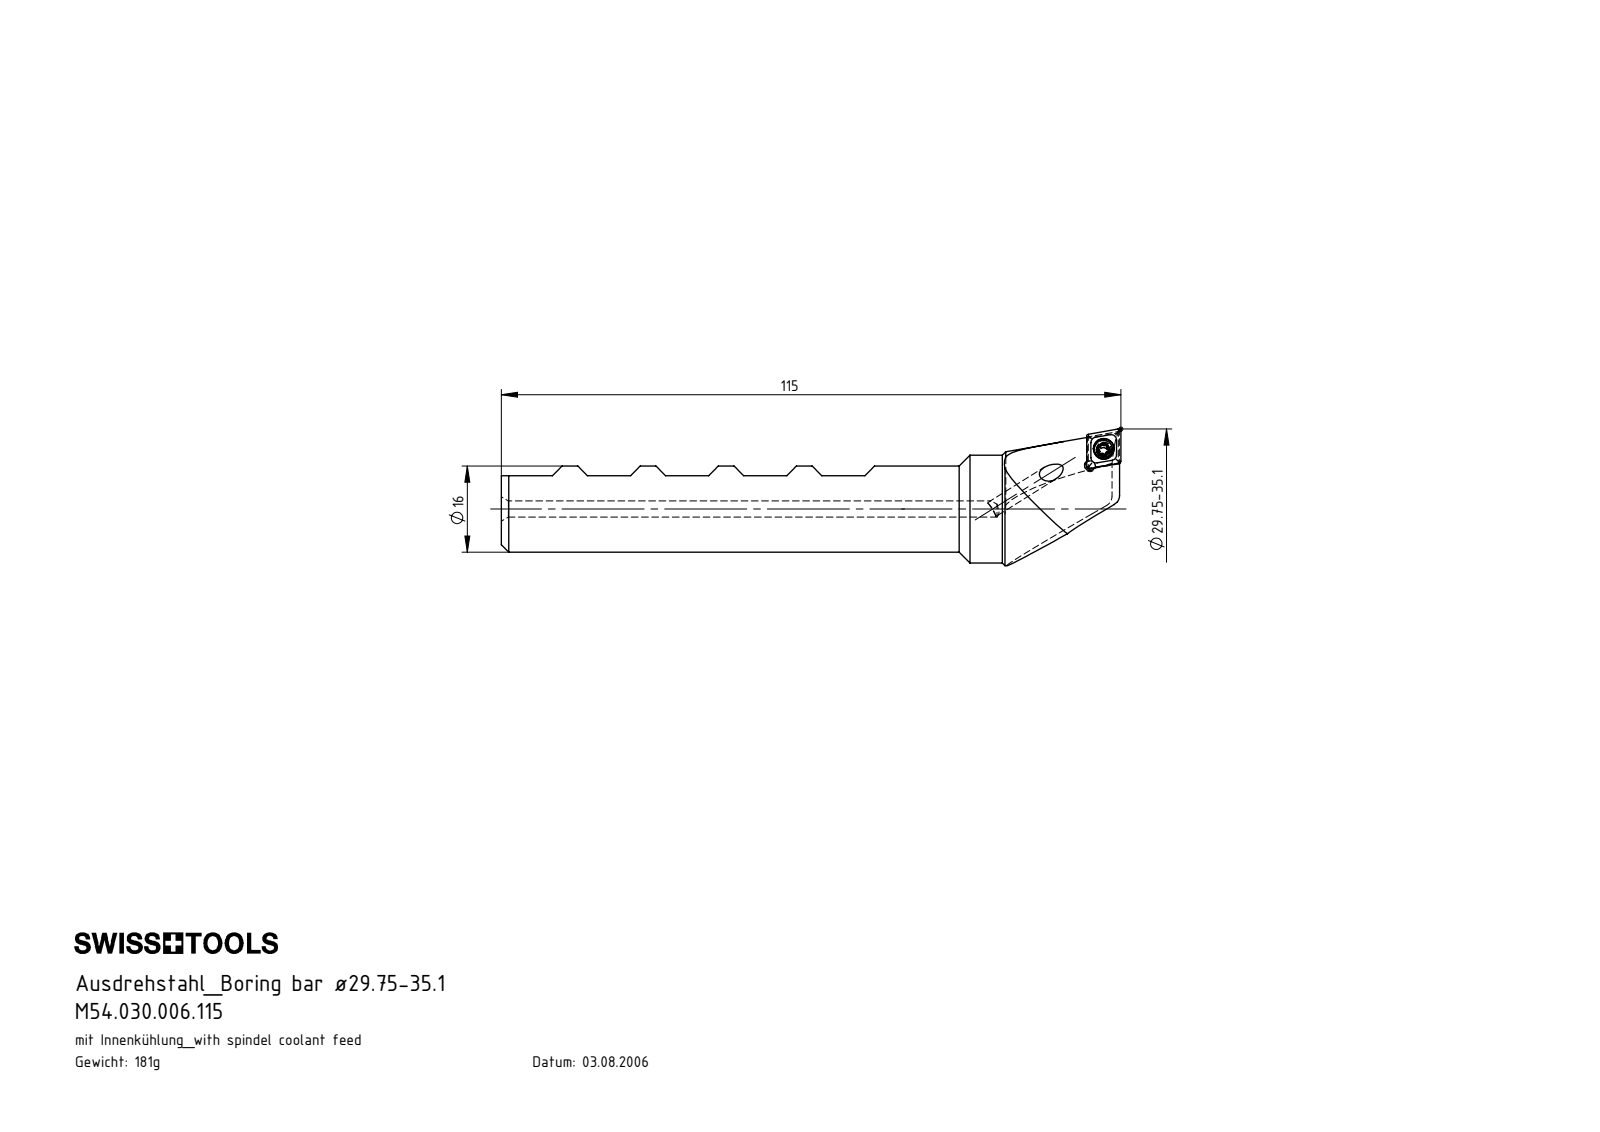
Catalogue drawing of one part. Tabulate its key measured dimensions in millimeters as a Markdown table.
| quantity | value |
| --- | --- |
| part name | CCMT060204; WCA-ER2.001.006_A; B30-WCA.K11.115_A; B30.WCA.K11.115 |
| STEP written by | SolidWorks 2017 (AUTOMOTIVE_DESIGN) |
| units | millimeters |
| bodies | 3 solids, 106 faces (42 planar, 25 cylindrical, 39 other) |
| overall size | 115 × 25.38 × 21.78 |
| volume | 23 010 mm³ |
| surface area | 7 654 mm² |
| round holes (diameter × count) | 3 × 2, 2 × 1, 2.05 × 1, 2.8 × 1, 3.85 × 1 |
| round bosses / shafts (diameter × count) | 20 × 1, 16 × 1, 3.4 × 1, 2.5 × 1 |
| partial cylindrical surfaces (radius × count) | 0.21 × 6, 0.36 × 5, 0.36 × 1, 2 × 1, 10.5 × 1, 12 × 1 |
| main face-to-face distances | 10.25, 20.5, 11.6, 30.76, 20.51, 9.41, 2.19, 9.42, 2.18, 30.75 |
| hole center spacings | 3.89, 3.99 |
